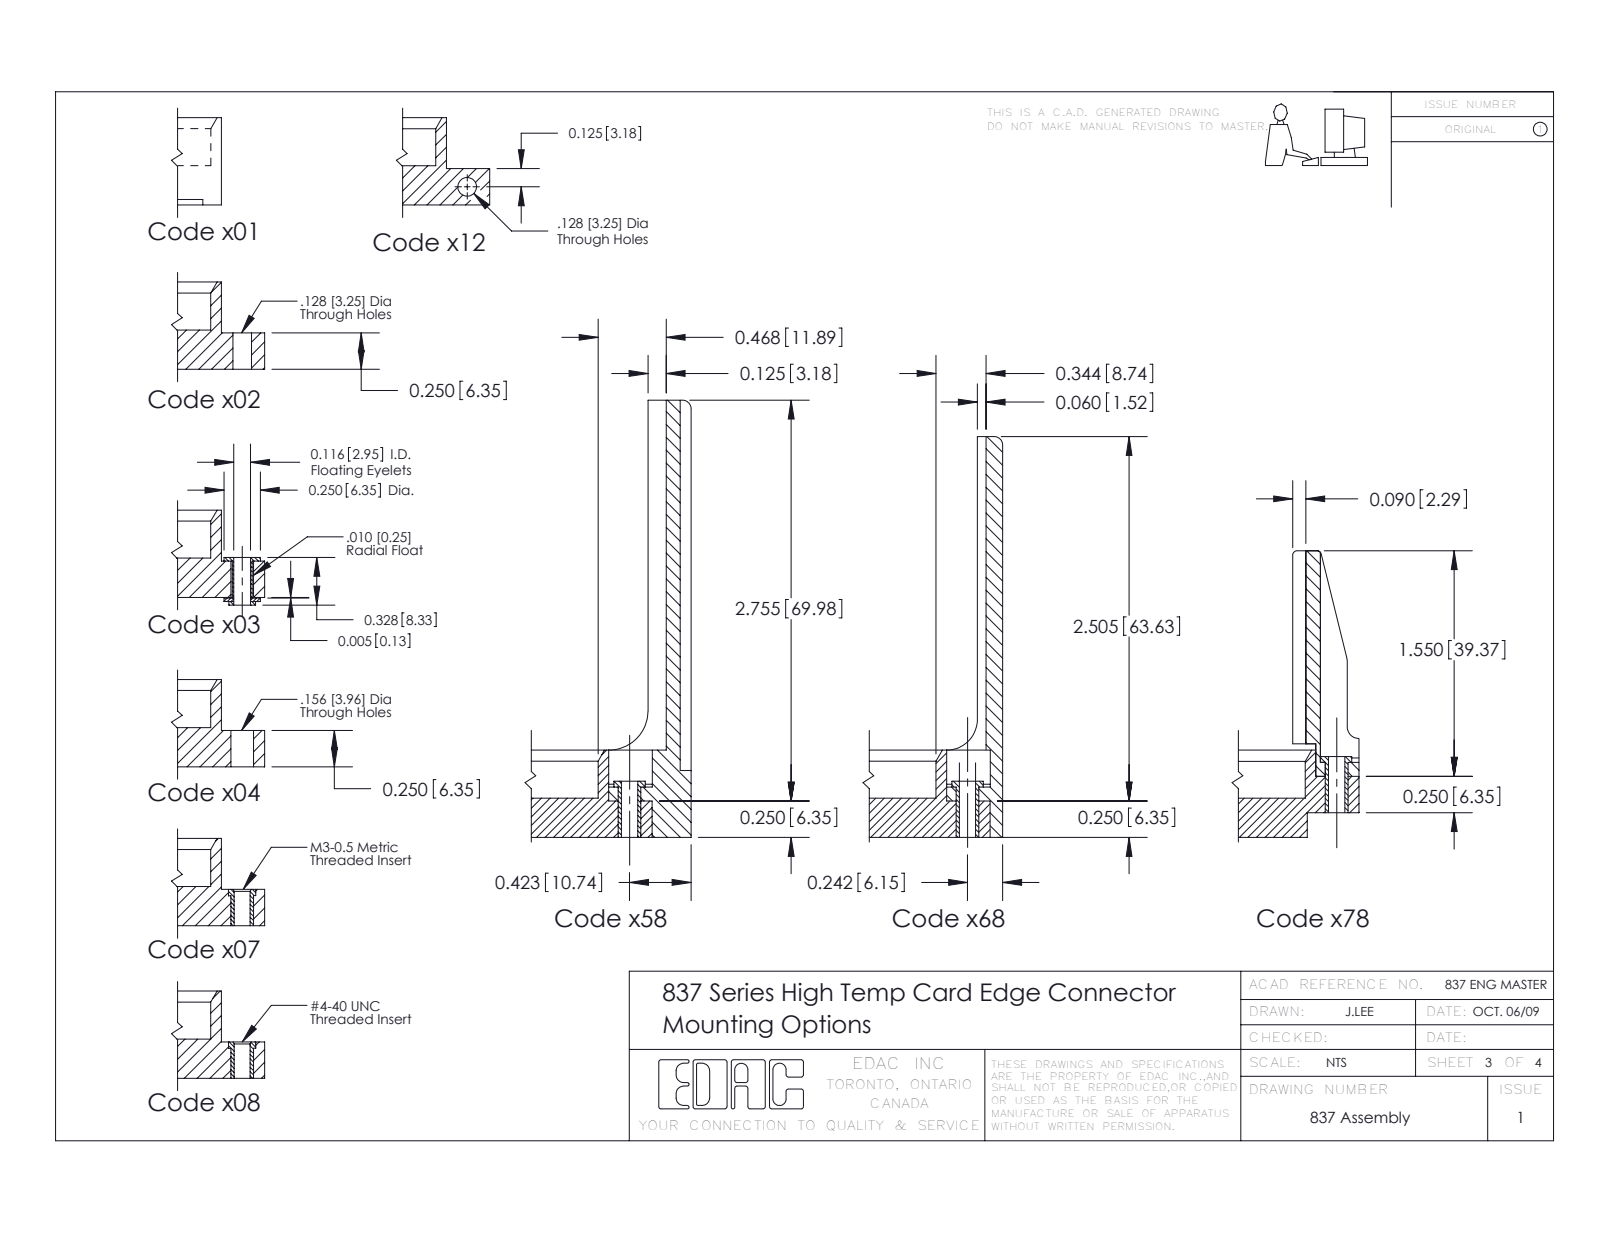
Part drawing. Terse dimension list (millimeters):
name: 345-292-001_345-293-100; 887-009-500-104; 837 Part_Flush Mounting Lugs - 0.156 Dia-TH
written by: SolidWorks 2020 (CONFIG_CONTROL_DESIGN)
unit: mm
bodies: 10 solids, 636 faces (430 planar, 206 cylindrical, 0 other)
size: 58.7 × 21.8 × 9.4
volume: 5 600 mm³; area: 5 423 mm²
holes: 2× ⌀4
rounds: 22× R0.3, 18× R0.2, 18× R0.4, 18× R0.5, 6× R0.2, 6× R0.8, 3× R0.7, 1× R0.4
face distances: 9.4, 1.8, 7.6, 5.1, 3.8, 4, 2.5, 6.9, 0.6, 1.3
hole spacings: 50.8
